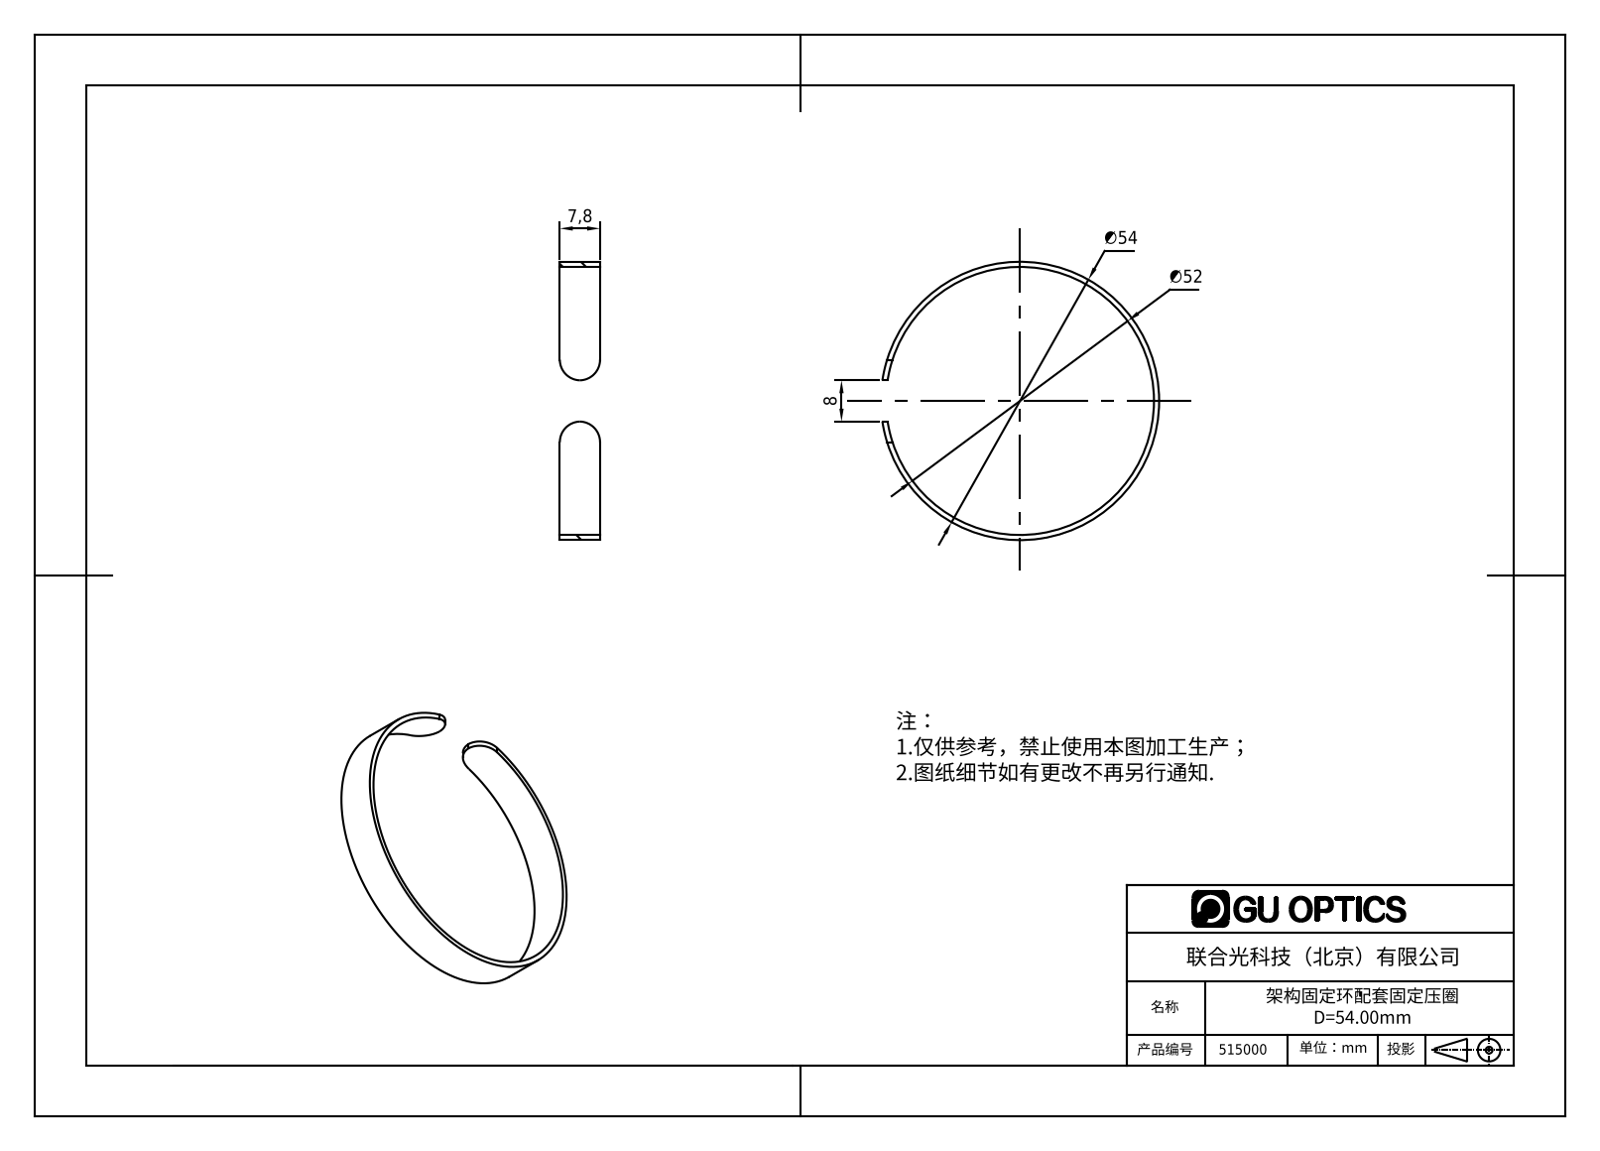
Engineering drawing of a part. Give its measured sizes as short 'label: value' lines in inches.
name: 515000
written by: SolidWorks 2016 (CONFIG_CONTROL_DESIGN)
unit: in
bodies: 1 solid, 12 faces (2 planar, 10 cylindrical, 0 other)
size: 2.126 × 2.114 × 0.307
volume: 0.075 in³; area: 4.294 in²
holes: 1× ⌀2.047
bosses: 1× ⌀2.126
rounds: 4× R0.157
face distances: 0.307
